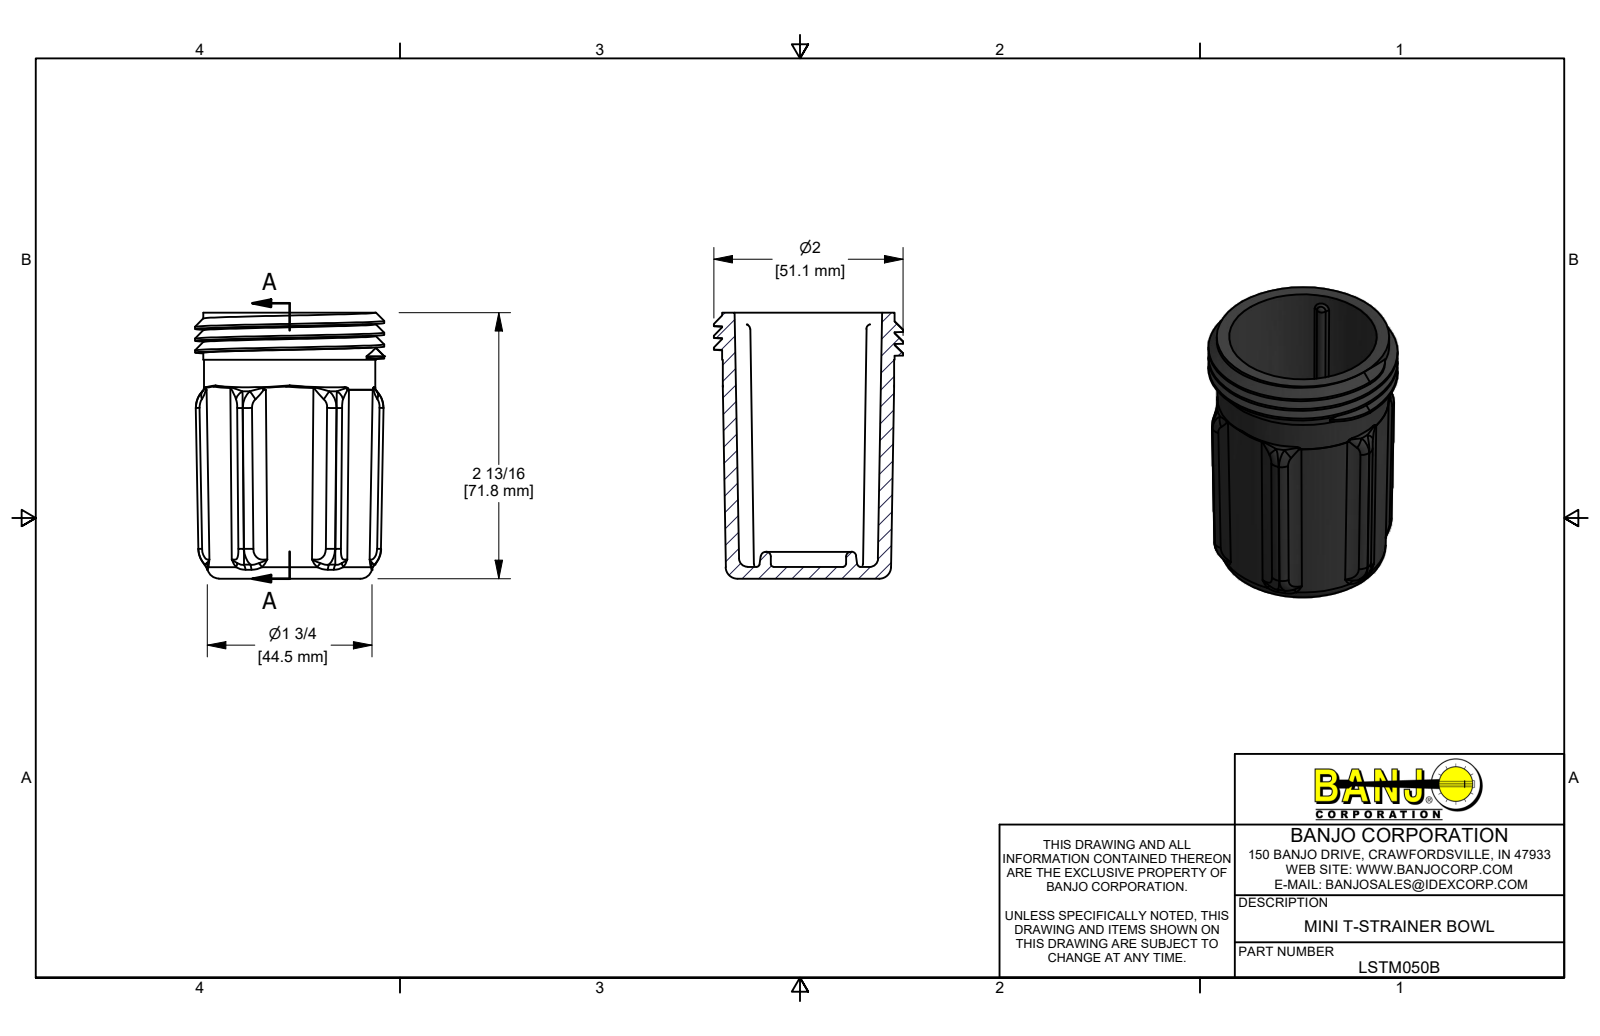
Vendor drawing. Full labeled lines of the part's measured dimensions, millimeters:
Part name (STEP PRODUCT): LSTM050B
STEP written by: Autodesk Inventor 2019 (AUTOMOTIVE_DESIGN)
Units: millimetres
Bodies: 1 solid, 200 faces (12 planar, 15 cylindrical, 173 other)
Overall size (bounding box): 71.8 × 51.1 × 51.1
Volume: 43 570 mm³ · Surface area: 24 150 mm²
Round holes (diameter × count): ⌀20.3 ×1
Round bosses / shafts (diameter × count): ⌀51.1 ×1, ⌀46.6 ×1, ⌀46.2 ×1
Partial cylindrical surfaces — rounded edges, fillets, slot ends (radius × count): R1.3 ×3, R14 ×1
Main face-to-face distances: 3.2, 71.8, 68.6, 59.1, 55.9, 12.7, 7.2, 4.1, 51.8, 64.5
